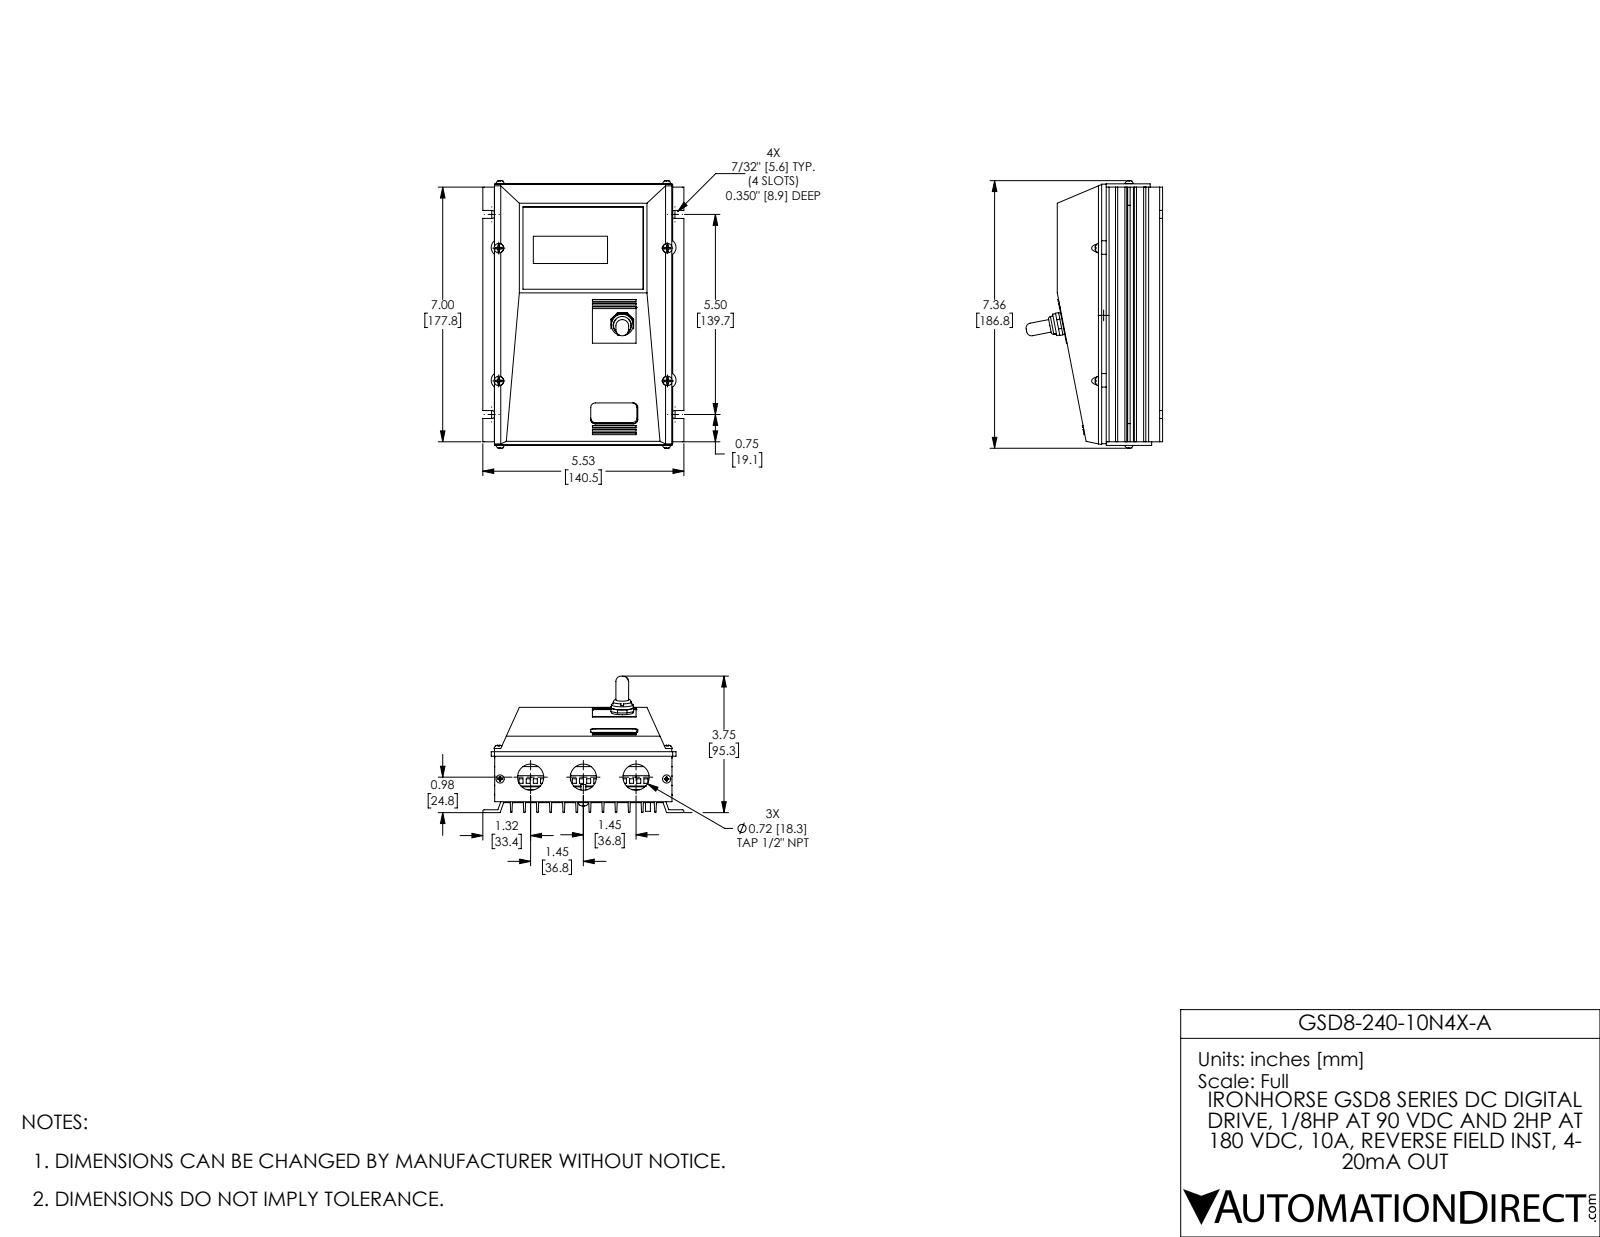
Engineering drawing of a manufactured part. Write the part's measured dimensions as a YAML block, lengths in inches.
part_name: "MD50E FINISHED ASSEMBLY Parrt Red1 R1 nc"
step_written_by: "SolidWorks 2017 (AUTOMOTIVE_DESIGN)"
units: inches
bodies: {solids: 30, faces: 2125, planar: 1318, cylindrical: 753, other: 54}
overall_size: [7.356, 5.53, 3.753]
volume: 19.17
surface_area: 465.7
round_holes:
  - {diameter: 0.055, count: 29}
  - {diameter: 0.035, count: 26}
  - {diameter: 0.04, count: 22}
  - {diameter: 0.157, count: 20}
  - {diameter: 0.033, count: 18}
  - {diameter: 0.055, count: 16}
  - {diameter: 0.15, count: 13}
  - {diameter: 0.064, count: 12}
  - {diameter: 0.14, count: 10}
  - {diameter: 0.046, count: 9}
  - {diameter: 0.1, count: 8}
  - {diameter: 0.079, count: 4}
round_bosses_or_shafts:
  - {diameter: 0.134, count: 6}
  - {diameter: 0.13, count: 4}
  - {diameter: 0.112, count: 4}
  - {diameter: 0.05, count: 4}
  - {diameter: 0.247, count: 3}
  - {diameter: 0.6, count: 1}
  - {diameter: 0.5, count: 1}
  - {diameter: 0.482, count: 1}
partial_cylinders:
  - {radius: 0.125, count: 16}
  - {radius: 0.02, count: 12}
  - {radius: 0.063, count: 12}
  - {radius: 0.021, count: 10}
  - {radius: 0.062, count: 10}
  - {radius: 0.126, count: 10}
  - {radius: 0.021, count: 6}
  - {radius: 0.04, count: 6}
face_to_face_distances: [0.1, 0.015, 0.719, 0.45, 0.35, 0.435, 0.335, 2.496, 1.175, 2.161]
hole_center_spacings: [0.498, 0.36, 0.197, 0.344, 0.345, 0.394, 0.498, 0.591]
